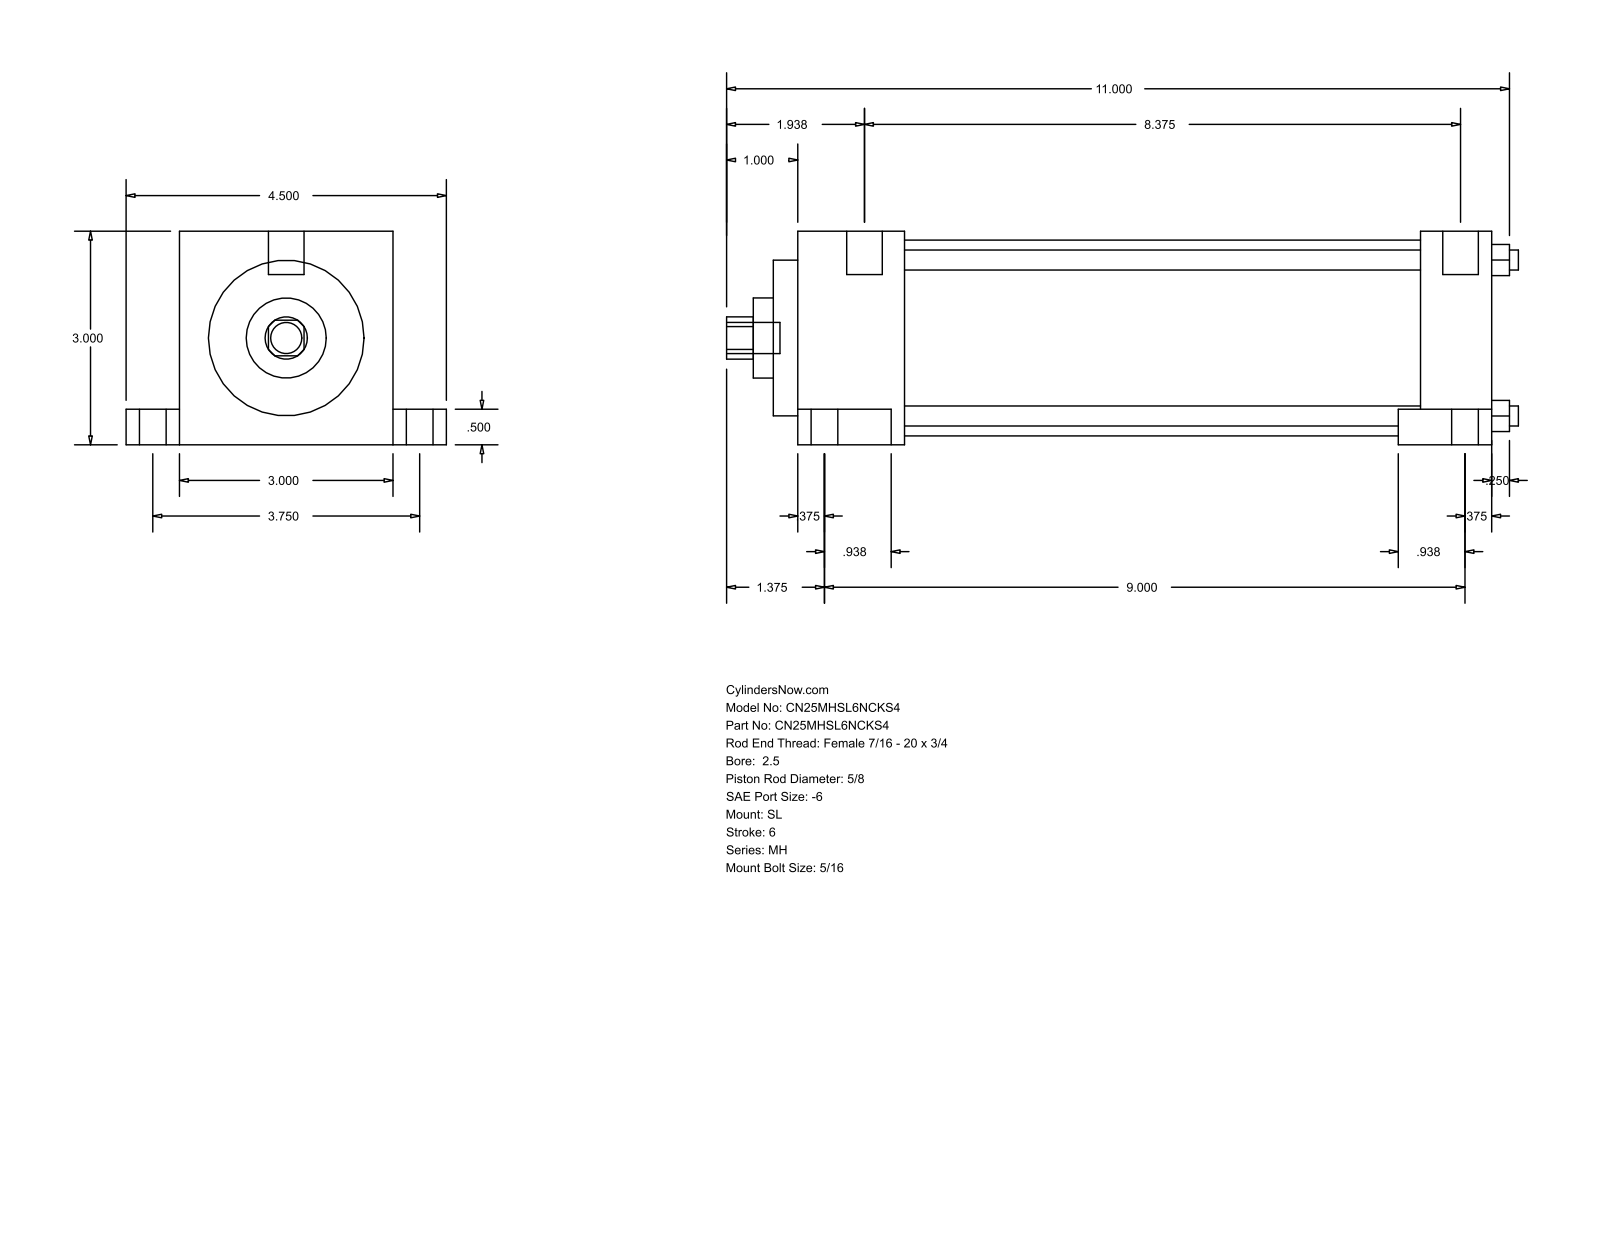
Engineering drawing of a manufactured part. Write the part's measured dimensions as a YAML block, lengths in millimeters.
part_name: "MH_SL__0250_0.625"
step_written_by: "GSSL Pune (CONFIG_CONTROL_DESIGN)"
units: millimeters
bodies: {solids: 0, faces: 86, planar: 61, cylindrical: 25, other: 0}
overall_size: [282.57, 114.3, 76.2]
round_holes:
  - {diameter: 7.14, count: 4}
  - {diameter: 15.88, count: 1}
  - {diameter: 28.57, count: 1}
  - {diameter: 55.55, count: 1}
  - {diameter: 69.85, count: 1}
round_bosses_or_shafts:
  - {diameter: 15.88, count: 2}
  - {diameter: 9.53, count: 2}
  - {diameter: 5.56, count: 2}
  - {diameter: 12.7, count: 1}
  - {diameter: 11.11, count: 1}
partial_cylinders:
  - {radius: 7.54, count: 1}
face_to_face_distances: [76.2, 25.4, 230.98, 256.38, 12.7, 63.5, 19.05, 95.25, 263.52, 31.75]
hole_center_spacings: [39.33, 55.62, 78.66]
